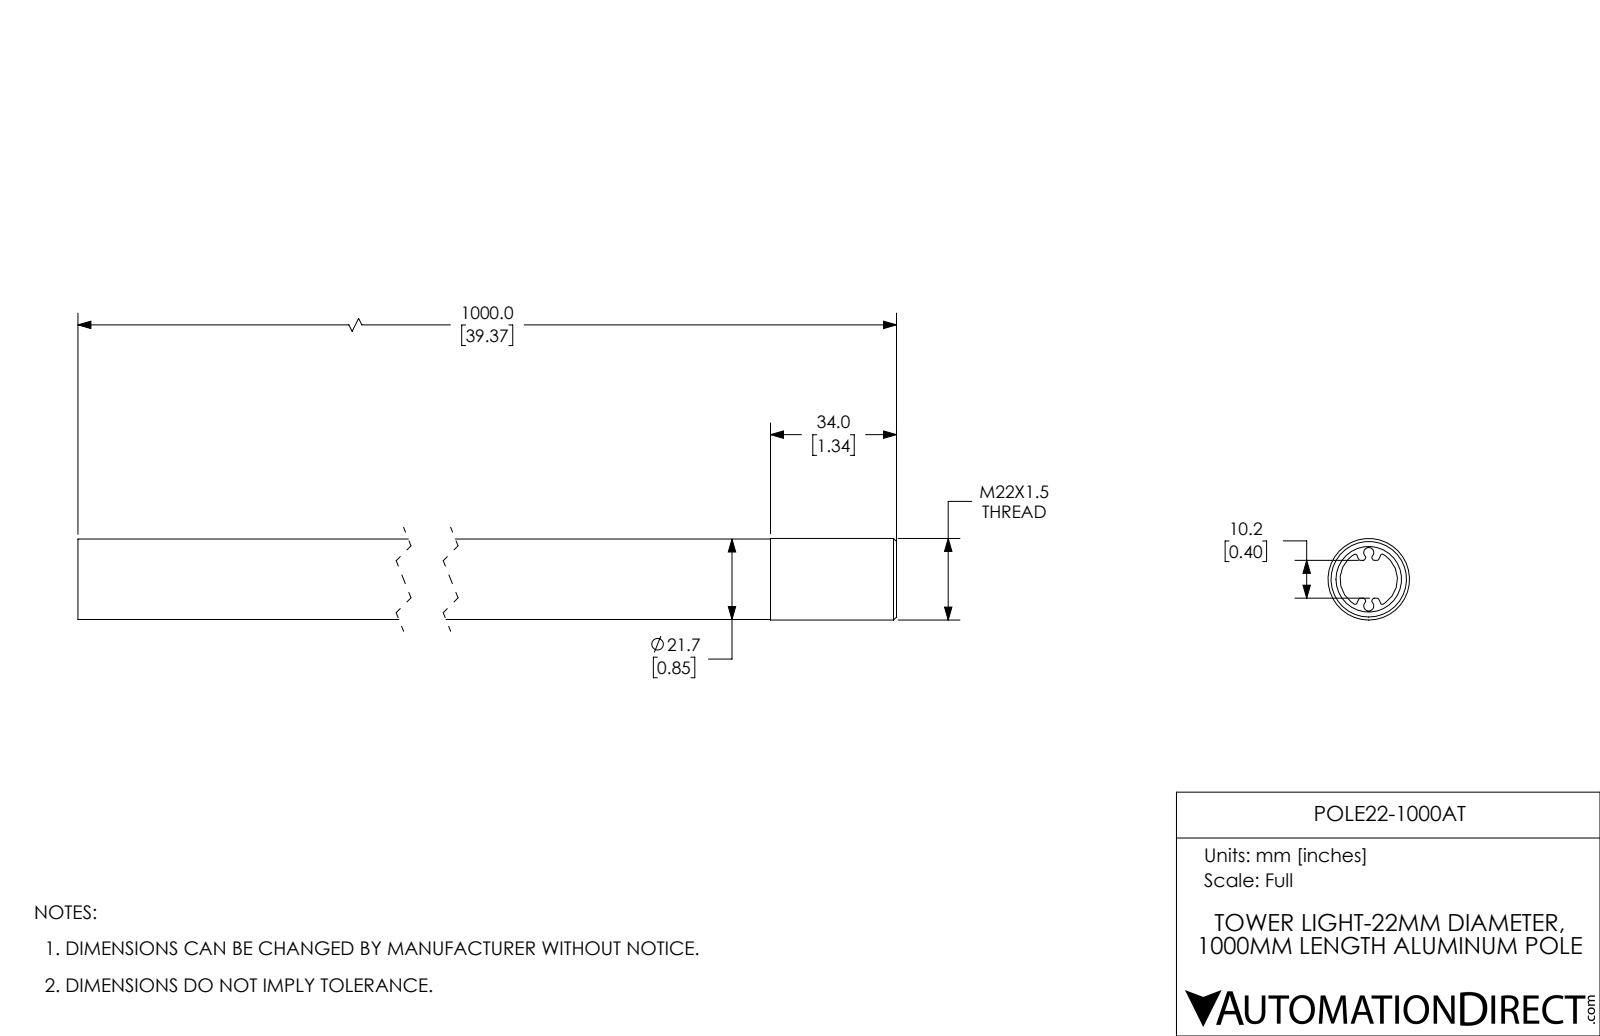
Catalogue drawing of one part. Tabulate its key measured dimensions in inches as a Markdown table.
| quantity | value |
| --- | --- |
| part name | POLE22-1000AT |
| STEP written by | SolidWorks 2017 (AUTOMOTIVE_DESIGN) |
| units | inches |
| bodies | 1 solid, 16 faces (4 planar, 6 cylindrical, 6 other) |
| overall size | 39.37 × 0.866 × 0.866 |
| volume | 11.88 in³ |
| surface area | 206.3 in² |
| round holes (diameter × count) | 0.697 × 1 |
| round bosses / shafts (diameter × count) | 0.866 × 1, 0.854 × 1 |
| main face-to-face distances | 39.37, 0.728, 38.642, 1.339, 0.61, 38.031 |
